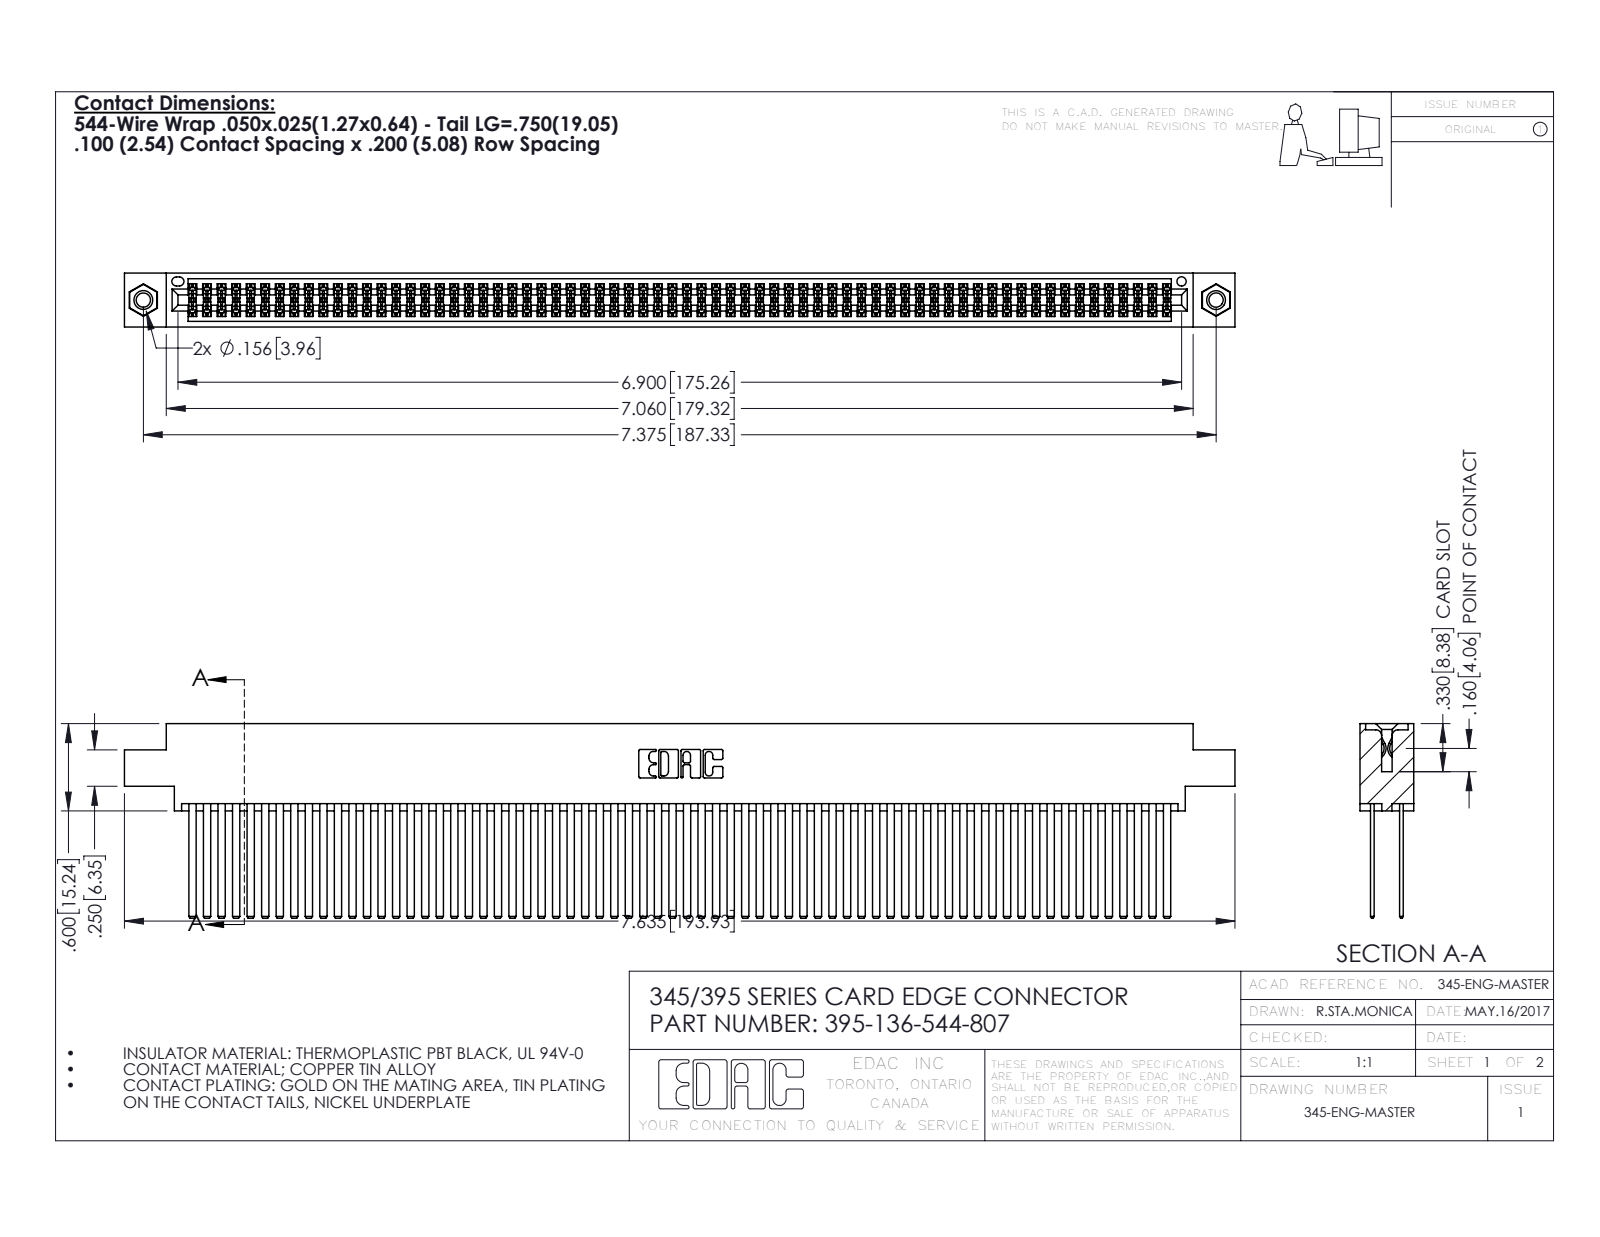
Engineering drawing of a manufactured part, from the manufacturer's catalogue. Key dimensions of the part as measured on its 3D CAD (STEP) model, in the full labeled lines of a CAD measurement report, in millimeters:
Part name (STEP PRODUCT): 345-250-001_345-250-005-103; 345 Part_0.170 Offset - 0.156 Dia-TI; 345-292-001_345-293-144; 395-136-544-807
STEP written by: SolidWorks 2016 (CONFIG_CONTROL_DESIGN)
Units: millimetres
Bodies: 139 solids, 6174 faces (4060 planar, 2098 cylindrical, 16 other)
Overall size (bounding box): 193.9 × 34 × 9.4
Volume: 20 860 mm³ · Surface area: 37 100 mm²
Round holes (diameter × count): ⌀2.5 ×2, ⌀3.2 ×2, ⌀4 ×2, ⌀1.6 ×1
Round bosses / shafts (diameter × count): ⌀3.9 ×2
Partial cylindrical surfaces — rounded edges, fillets, slot ends (radius × count): R0.2 ×204, R0.3 ×22, R0.2 ×6, R0.8 ×6, R0.7 ×3, R0.4 ×2, R0.5 ×2, R0.6 ×2
Main face-to-face distances: 5.1, 0.6, 1.8, 2.5, 6.9, 7.6, 5.7, 4.4, 9.4, 3.8
Hole centre spacings: 6.9, 181.3, 187.3
